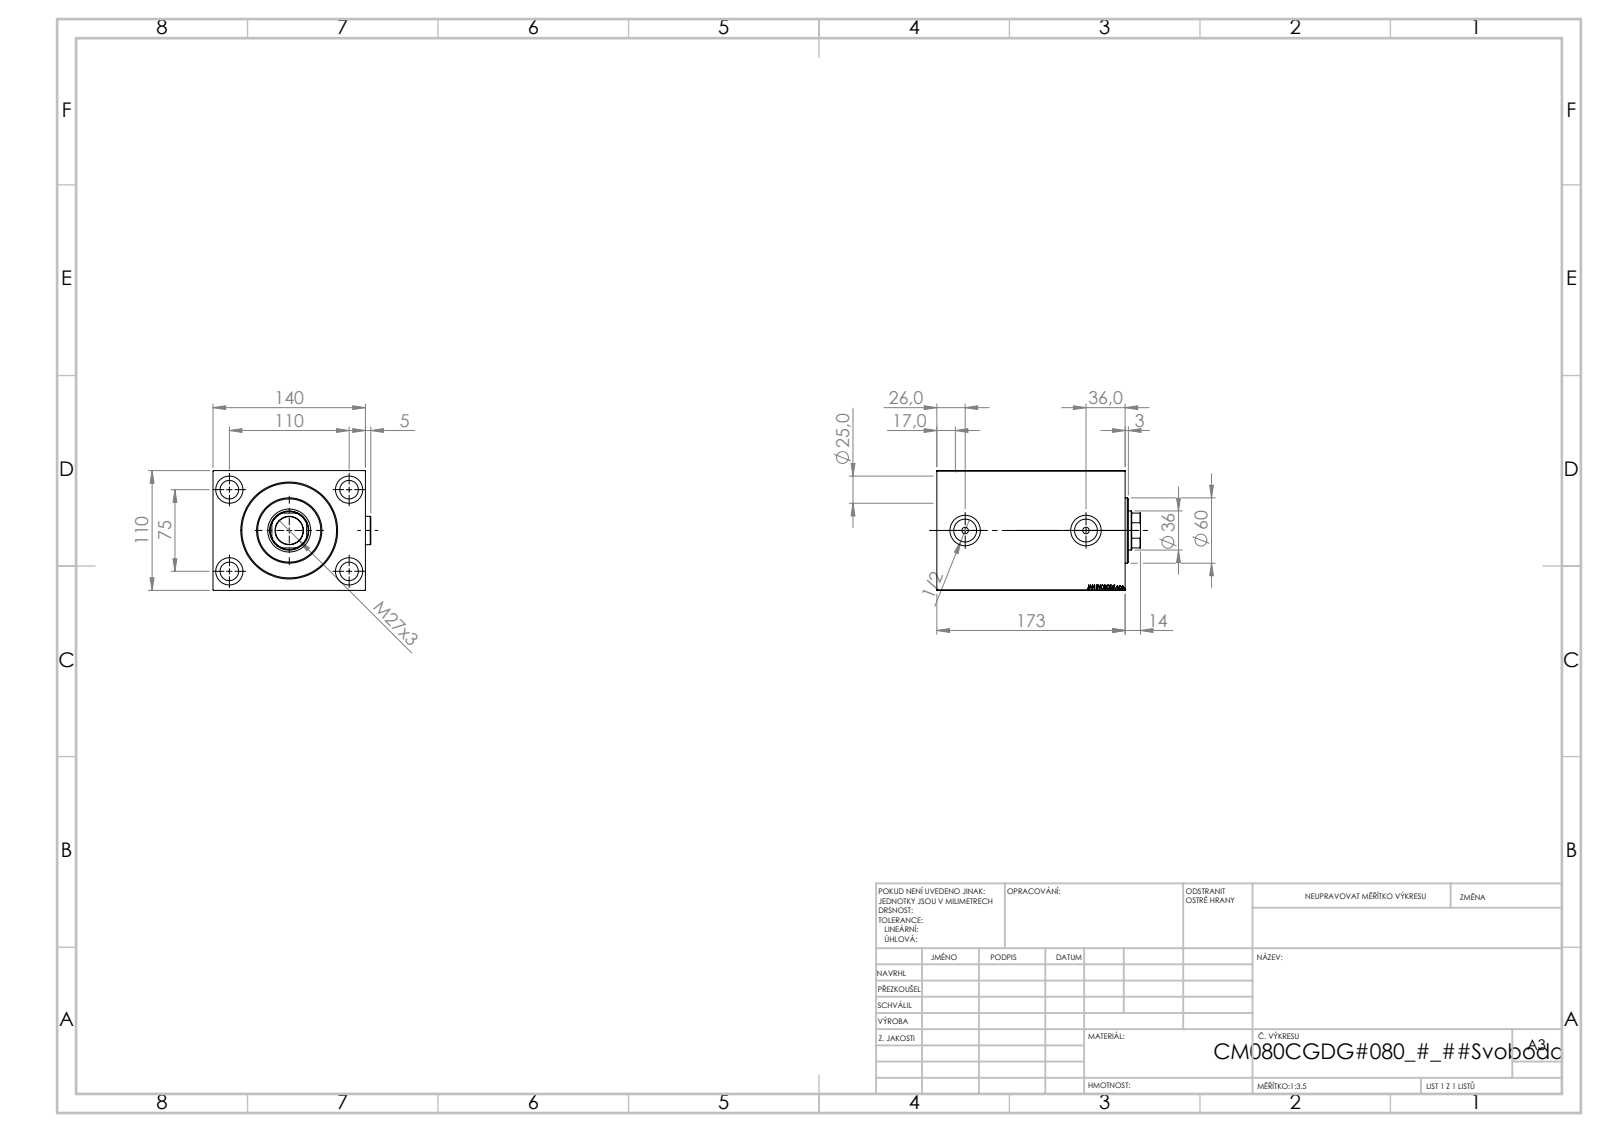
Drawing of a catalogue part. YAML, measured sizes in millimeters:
part_name: "V450CM_C_VCP; Zatka_OIL_PORT; V450CM_C_Body; V450CM_VC_B"
step_written_by: "SolidWorks 2019 (CONFIG_CONTROL_DESIGN)"
units: millimeters
bodies: {solids: 5, faces: 919, planar: 443, cylindrical: 78, other: 398}
overall_size: [187, 144.9, 110]
volume: 2136000
surface_area: 256918
round_holes:
  - {diameter: 17, count: 4}
  - {diameter: 25, count: 4}
  - {diameter: 6, count: 2}
  - {diameter: 20.96, count: 2}
  - {diameter: 28, count: 2}
  - {diameter: 25.5, count: 1}
  - {diameter: 36, count: 1}
  - {diameter: 39.5, count: 1}
  - {diameter: 80, count: 1}
  - {diameter: 82, count: 1}
  - {diameter: 87, count: 1}
round_bosses_or_shafts:
  - {diameter: 26, count: 2}
  - {diameter: 60, count: 1}
partial_cylinders:
  - {radius: 17.5, count: 1}
face_to_face_distances: [110, 140, 173, 152, 21, 159, 14, 138, 94, 80]
hole_center_spacings: [66.57, 75, 110, 133.14, 111]
